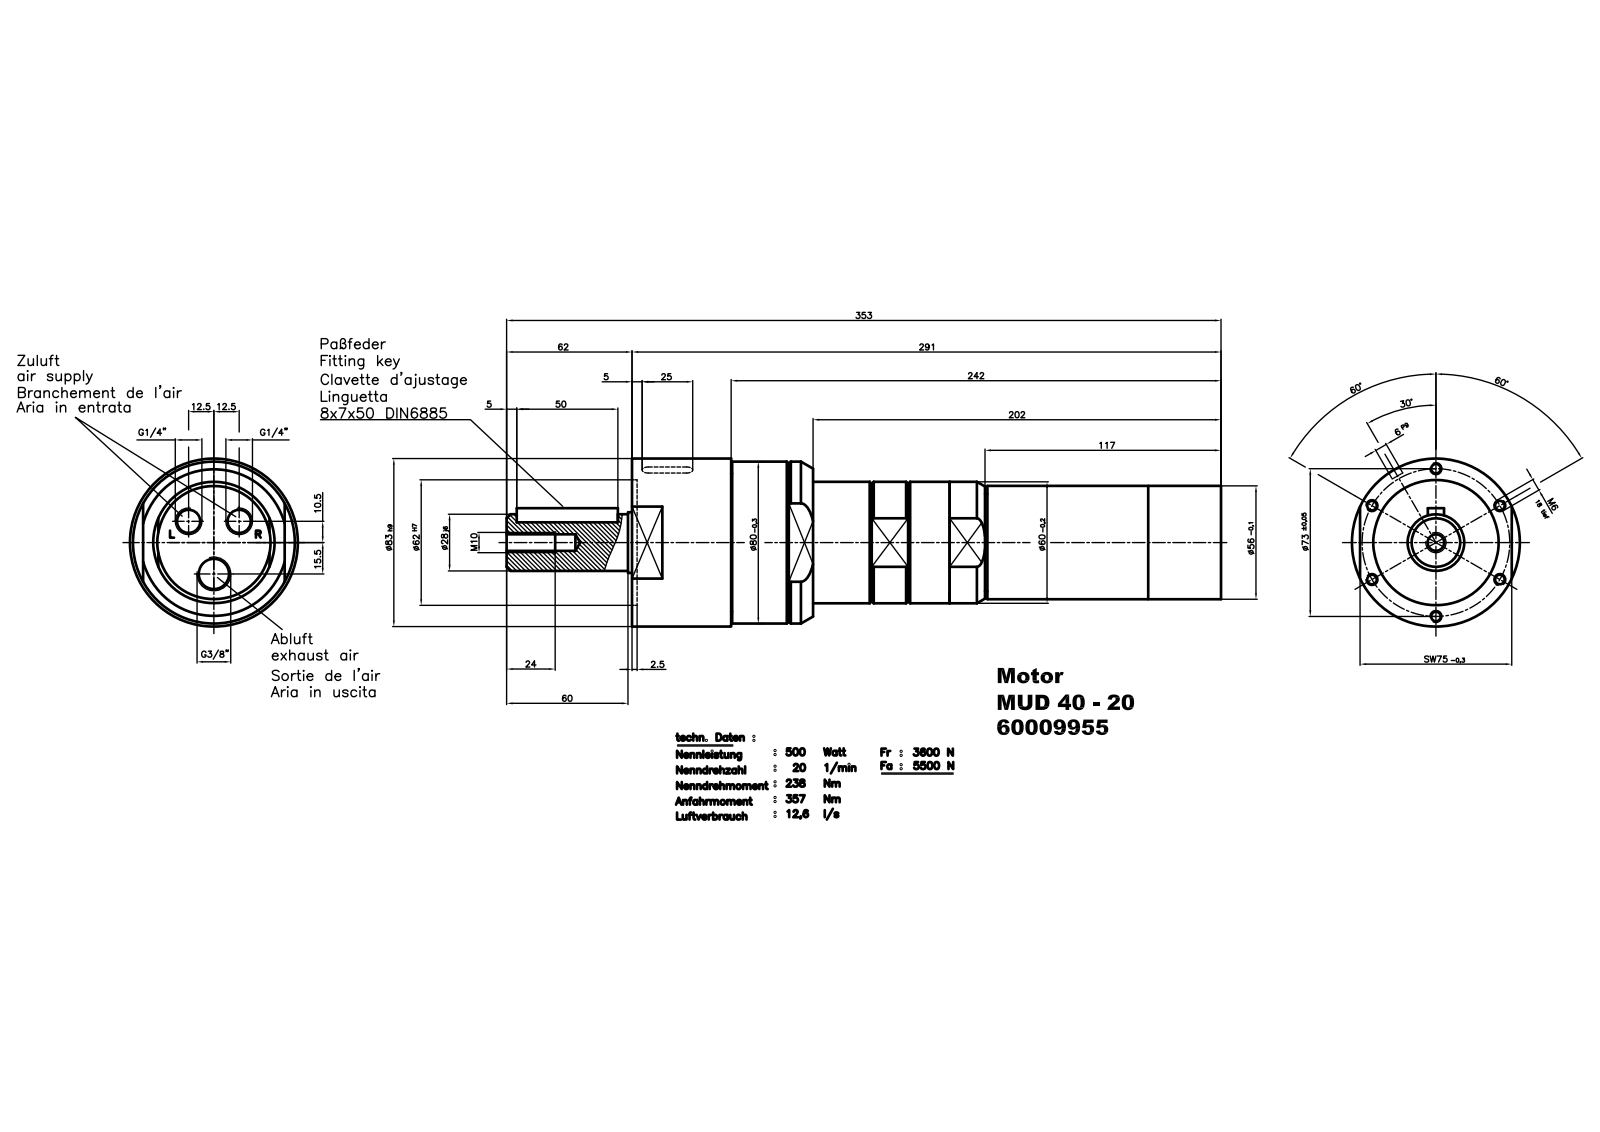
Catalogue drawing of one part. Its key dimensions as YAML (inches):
part_name: "MUD 40-20_60009955"
step_written_by: "Autodesk Inventor 2008 (AUTOMOTIVE_DESIGN)"
units: inches
bodies: {solids: 1, faces: 373, planar: 135, cylindrical: 184, other: 54}
overall_size: [13.906, 3.268, 3.268]
volume: 60.96
surface_area: 151.9
round_holes:
  - {diameter: 0.061, count: 2}
  - {diameter: 0.157, count: 2}
  - {diameter: 0.217, count: 2}
  - {diameter: 1.496, count: 1}
  - {diameter: 2.311, count: 1}
  - {diameter: 2.441, count: 1}
  - {diameter: 2.559, count: 1}
round_bosses_or_shafts:
  - {diameter: 0.197, count: 2}
  - {diameter: 0.142, count: 2}
  - {diameter: 3.268, count: 1}
  - {diameter: 3.15, count: 1}
  - {diameter: 2.684, count: 1}
  - {diameter: 2.362, count: 1}
  - {diameter: 2.205, count: 1}
  - {diameter: 1.897, count: 1}
partial_cylinders:
  - {radius: 0.207, count: 68}
  - {radius: 0.089, count: 2}
  - {radius: 0.118, count: 2}
  - {radius: 0.157, count: 2}
  - {radius: 1.042, count: 1}
  - {radius: 1.117, count: 1}
  - {radius: 1.28, count: 1}
  - {radius: 1.366, count: 1}
face_to_face_distances: [11.465, 1.929, 9.535, 0.02, 1.752, 0.197, 3.524, 1.594, 7.941, 1.732]
